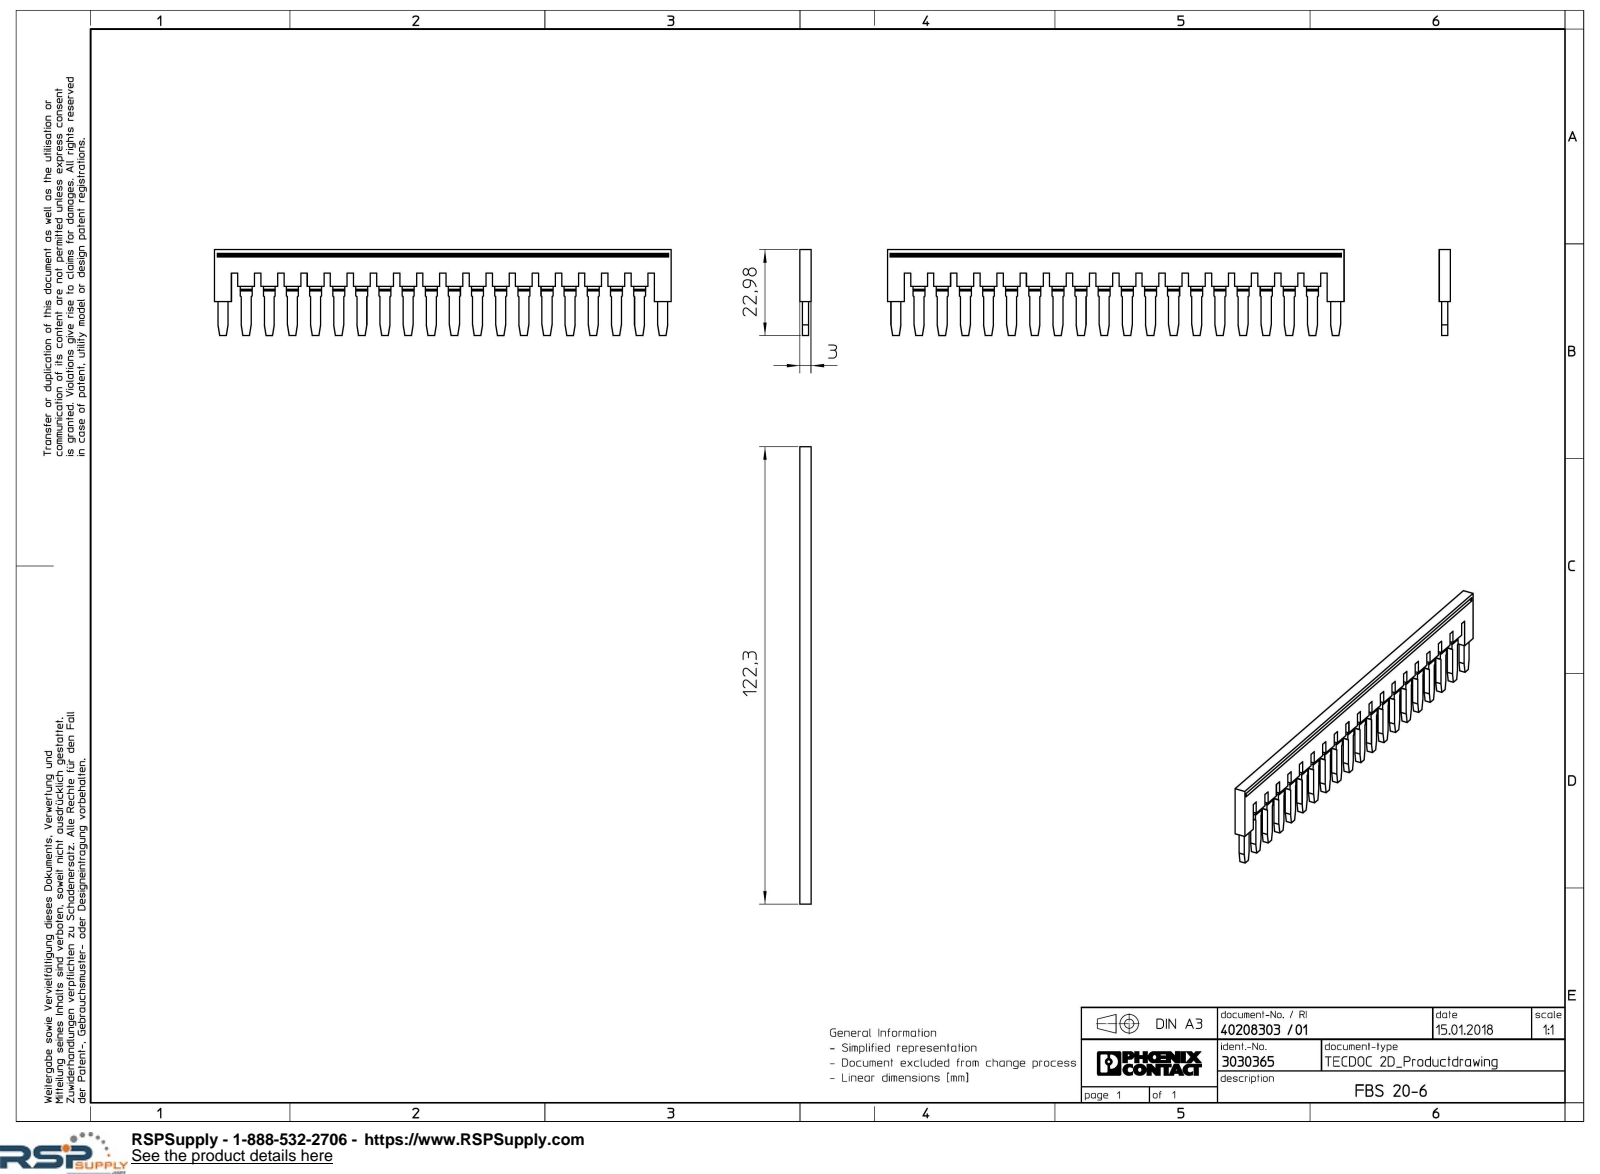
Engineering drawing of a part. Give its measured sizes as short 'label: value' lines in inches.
name: FBS_20-6_select
written by: Creo Elements/Direct Modeling 20.1A 29-Sep-2018 (C) Parametric Technology GmbH (AUTOMOTIVE_DESIGN)
unit: in
bodies: 1 solid, 412 faces (412 planar, 0 cylindrical, 0 other)
size: 4.815 × 0.905 × 0.118
volume: 0.262 in³; area: 9.325 in²
face distances: 0.028, 0.091, 0.118, 0.063, 0.244, 0.488, 0.241, 0.732, 0.386, 0.482
